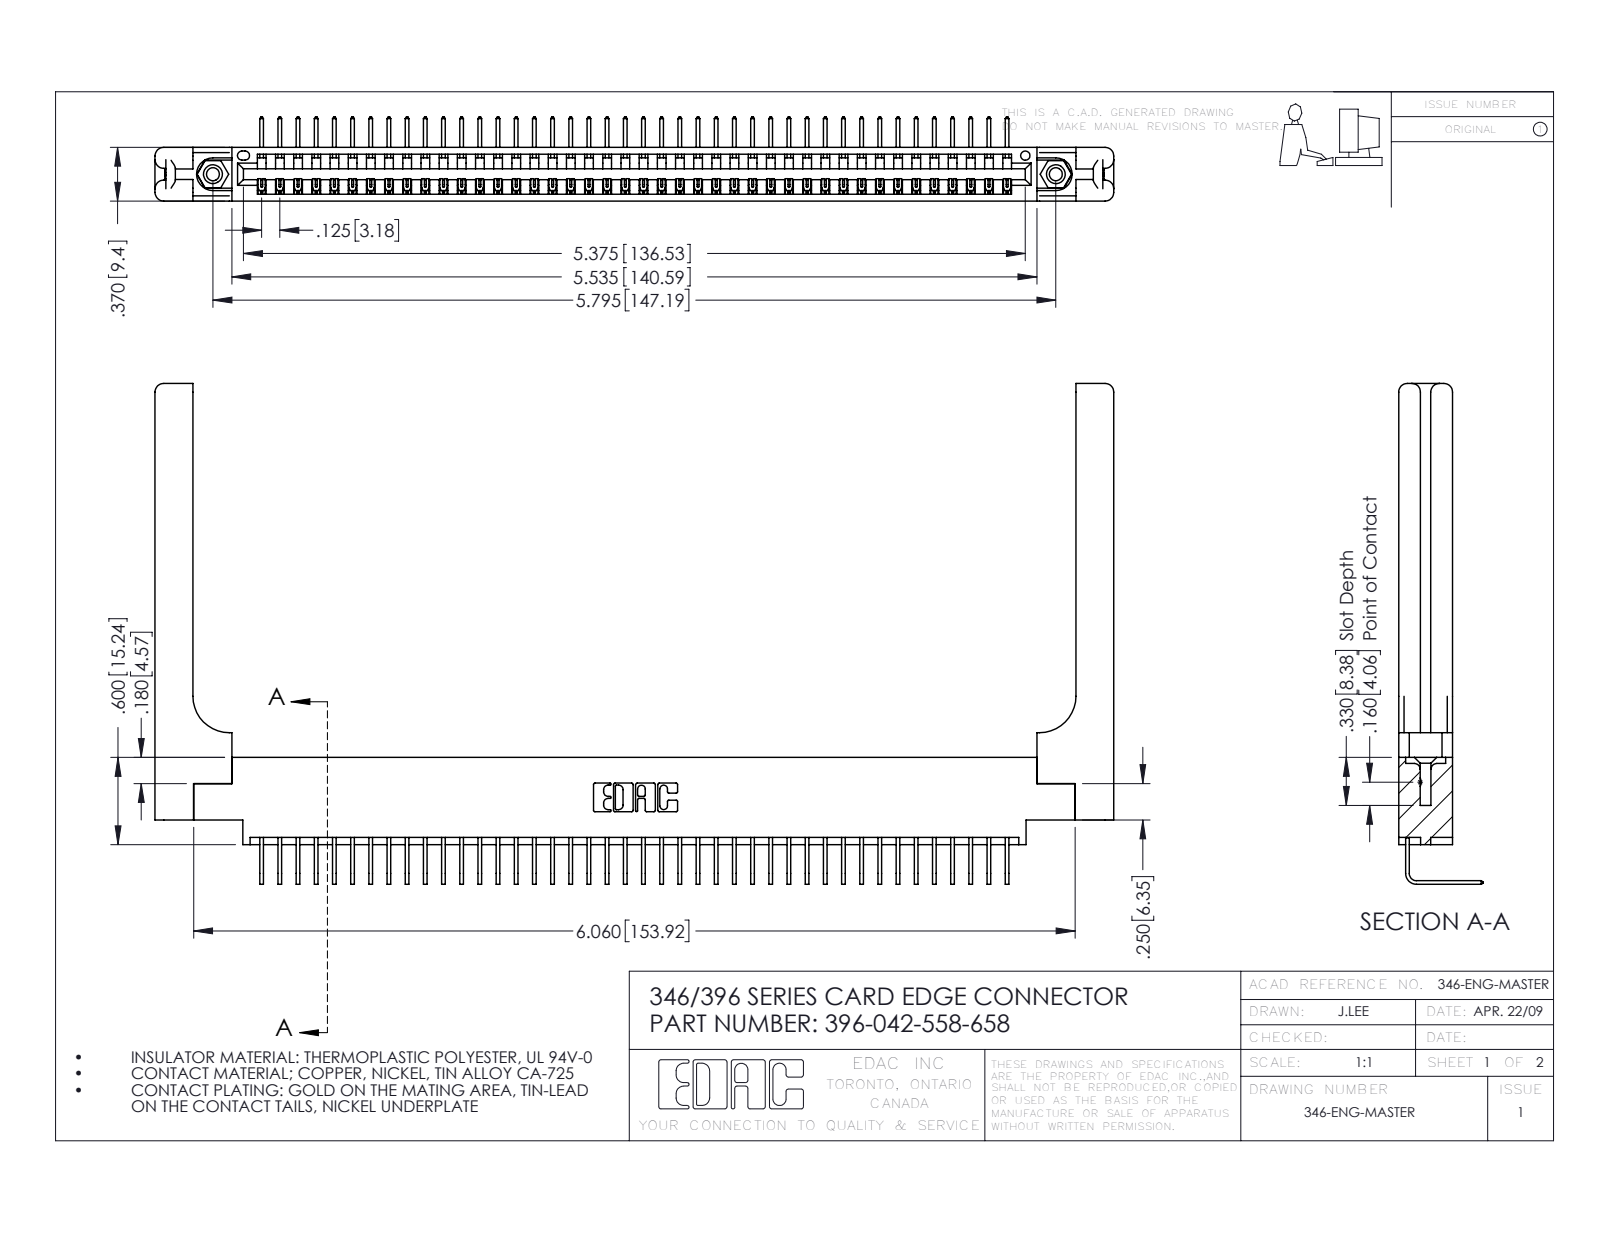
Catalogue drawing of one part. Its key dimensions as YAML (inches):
part_name: "345-250-001_345-250-001-102; 346-220-058_345-220-058; 346 Part_0.170 Offset - 0.156 Dia-TH; 396-042-558-658 (+1 more)"
step_written_by: "SolidWorks 2016 (CONFIG_CONTROL_DESIGN)"
units: inches
bodies: {solids: 47, faces: 2902, planar: 1992, cylindrical: 850, other: 60}
overall_size: [6.591, 3.443, 0.58]
volume: 1.436
surface_area: 40.57
round_holes:
  - {diameter: 0.089, count: 2}
  - {diameter: 0.125, count: 2}
  - {diameter: 0.156, count: 2}
  - {diameter: 0.064, count: 1}
round_bosses_or_shafts:
  - {diameter: 0.155, count: 2}
partial_cylinders:
  - {radius: 0.006, count: 84}
  - {radius: 0.01, count: 22}
  - {radius: 0.06, count: 16}
  - {radius: 0.007, count: 6}
  - {radius: 0.031, count: 6}
  - {radius: 0.026, count: 3}
  - {radius: 0.03, count: 2}
  - {radius: 0.031, count: 2}
face_to_face_distances: [0.37, 0.322, 0.048, 0.072, 0.148, 0.15, 0.025, 0.298, 0.25, 0.222]
hole_center_spacings: [0.246, 5.586, 5.795]
